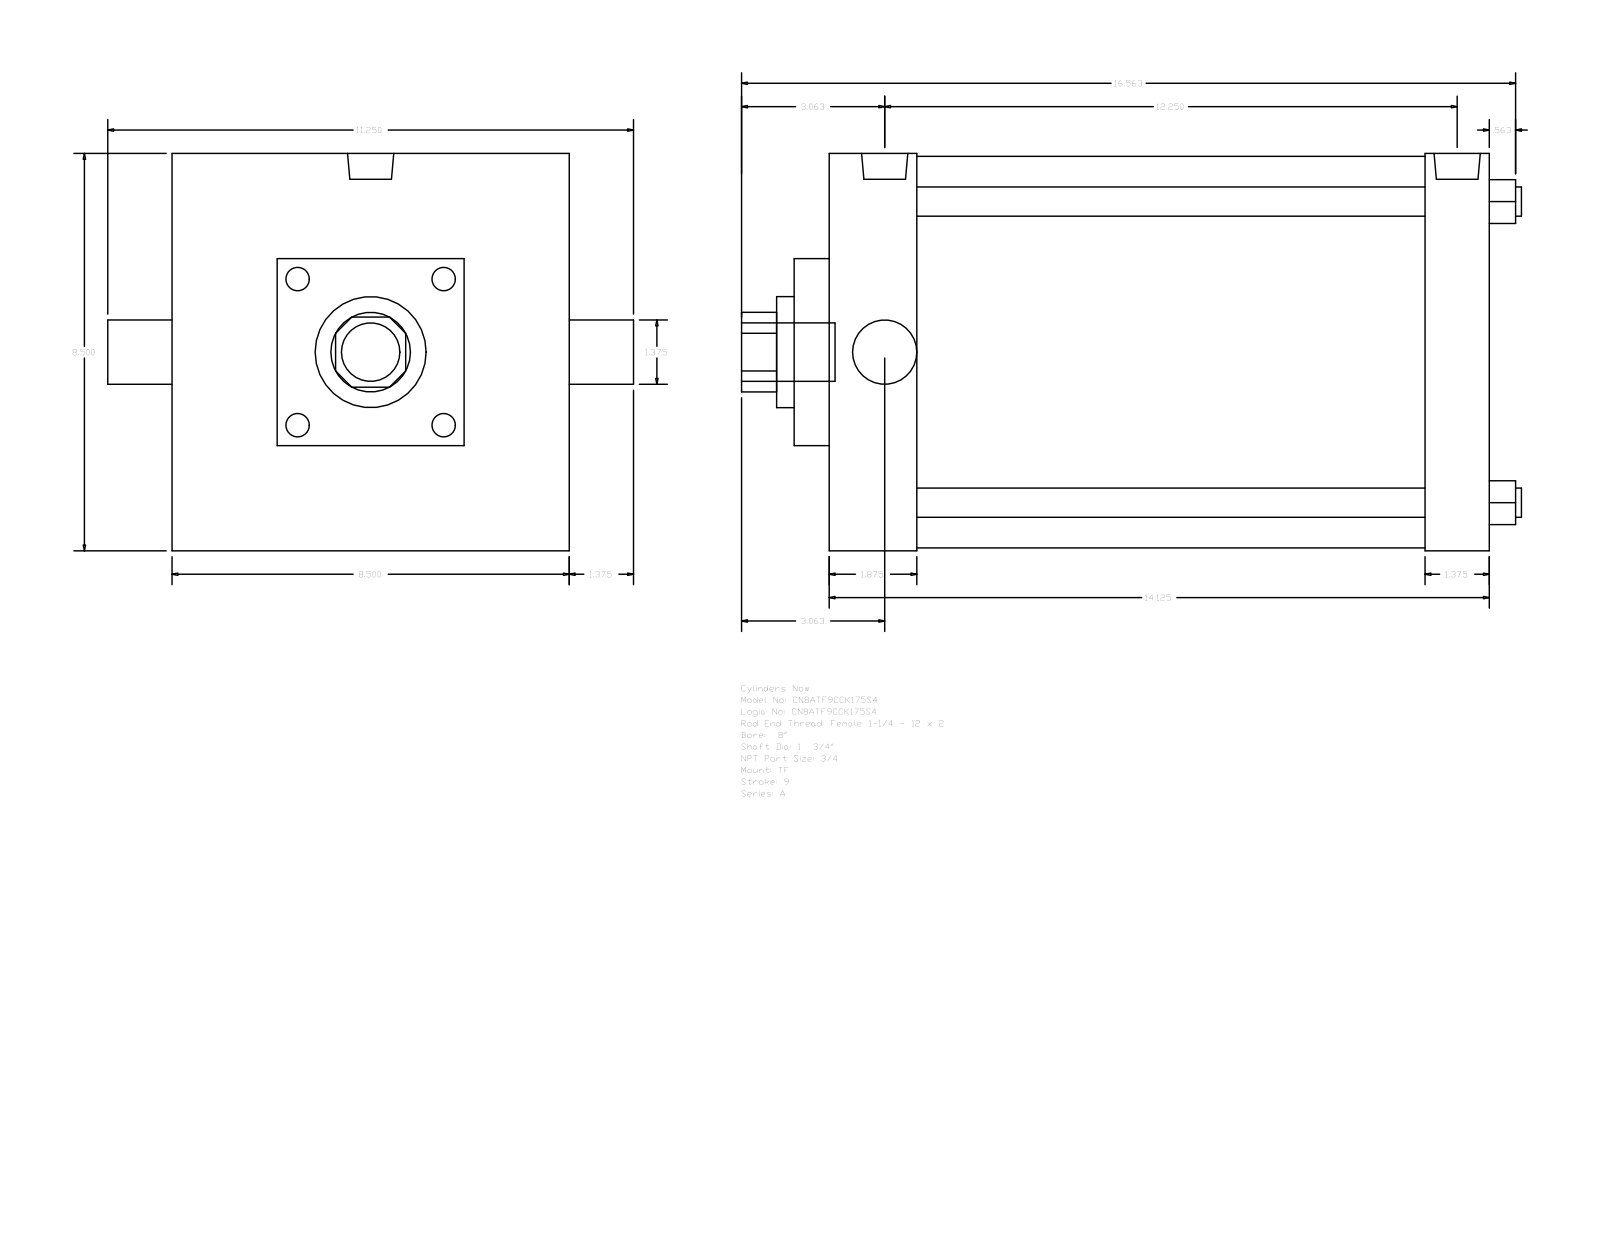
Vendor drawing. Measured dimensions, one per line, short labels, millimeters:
name: A_TF__0800_1.75
written by: GSSL Pune (CONFIG_CONTROL_DESIGN)
unit: mm
bodies: 0 solids, 89 faces (65 planar, 24 cylindrical, 0 other)
size: 423.86 × 285.75 × 215.9
holes: 4× ⌀15.88, 1× ⌀34.92, 1× ⌀44.45, 1× ⌀60.33, 1× ⌀212.72
bosses: 3× ⌀15.08, 2× ⌀25.12, 1× ⌀31.75
rounds: 1× R21.63
face distances: 358.78, 215.9, 34.92, 47.63, 311.15, 323.86, 276.23, 19.05, 57.15, 158.75
hole spacings: 115.67, 163.58, 231.34
